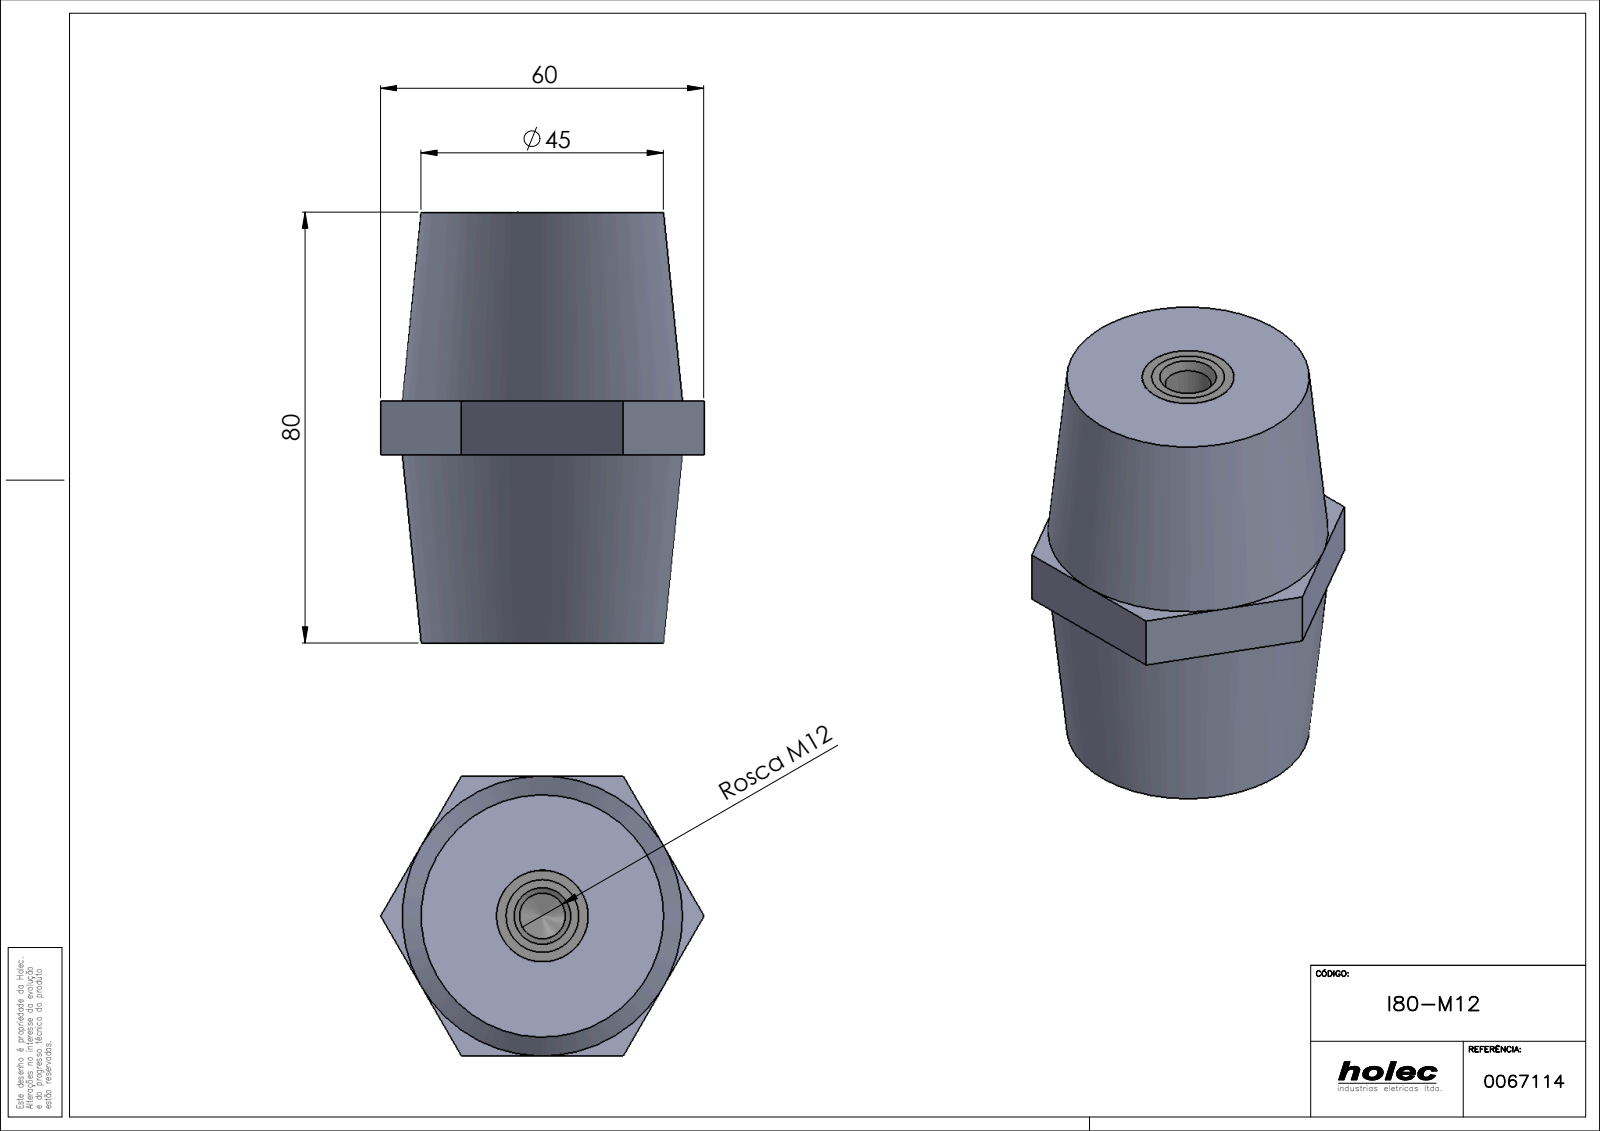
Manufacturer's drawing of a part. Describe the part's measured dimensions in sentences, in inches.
The part is named "PB1_0110(PB1_0111_12); PB1_0003; I80-M12; PB1_0002". Its 3-D file was written by "SolidWorks 2017 (AUTOMOTIVE_DESIGN)". It is 5 solids with 238 faces: 114 planar, 20 cylindrical and 104 other. Overall it measures 3.15 by 2.364 by 2.047 inches. Its volume is 9.499 cubic inches and its surface area 41.29 square inches. Round holes: 1 of diameter 0.335, 1 of diameter 0.402. Round bosses or shafts: 1 of diameter 0.551. The main face-to-face distances are 0.669, 3.15, 2.047, 2.402, 2.402, 2.48, 0.217, 0.748, 0.748, 0.078.
